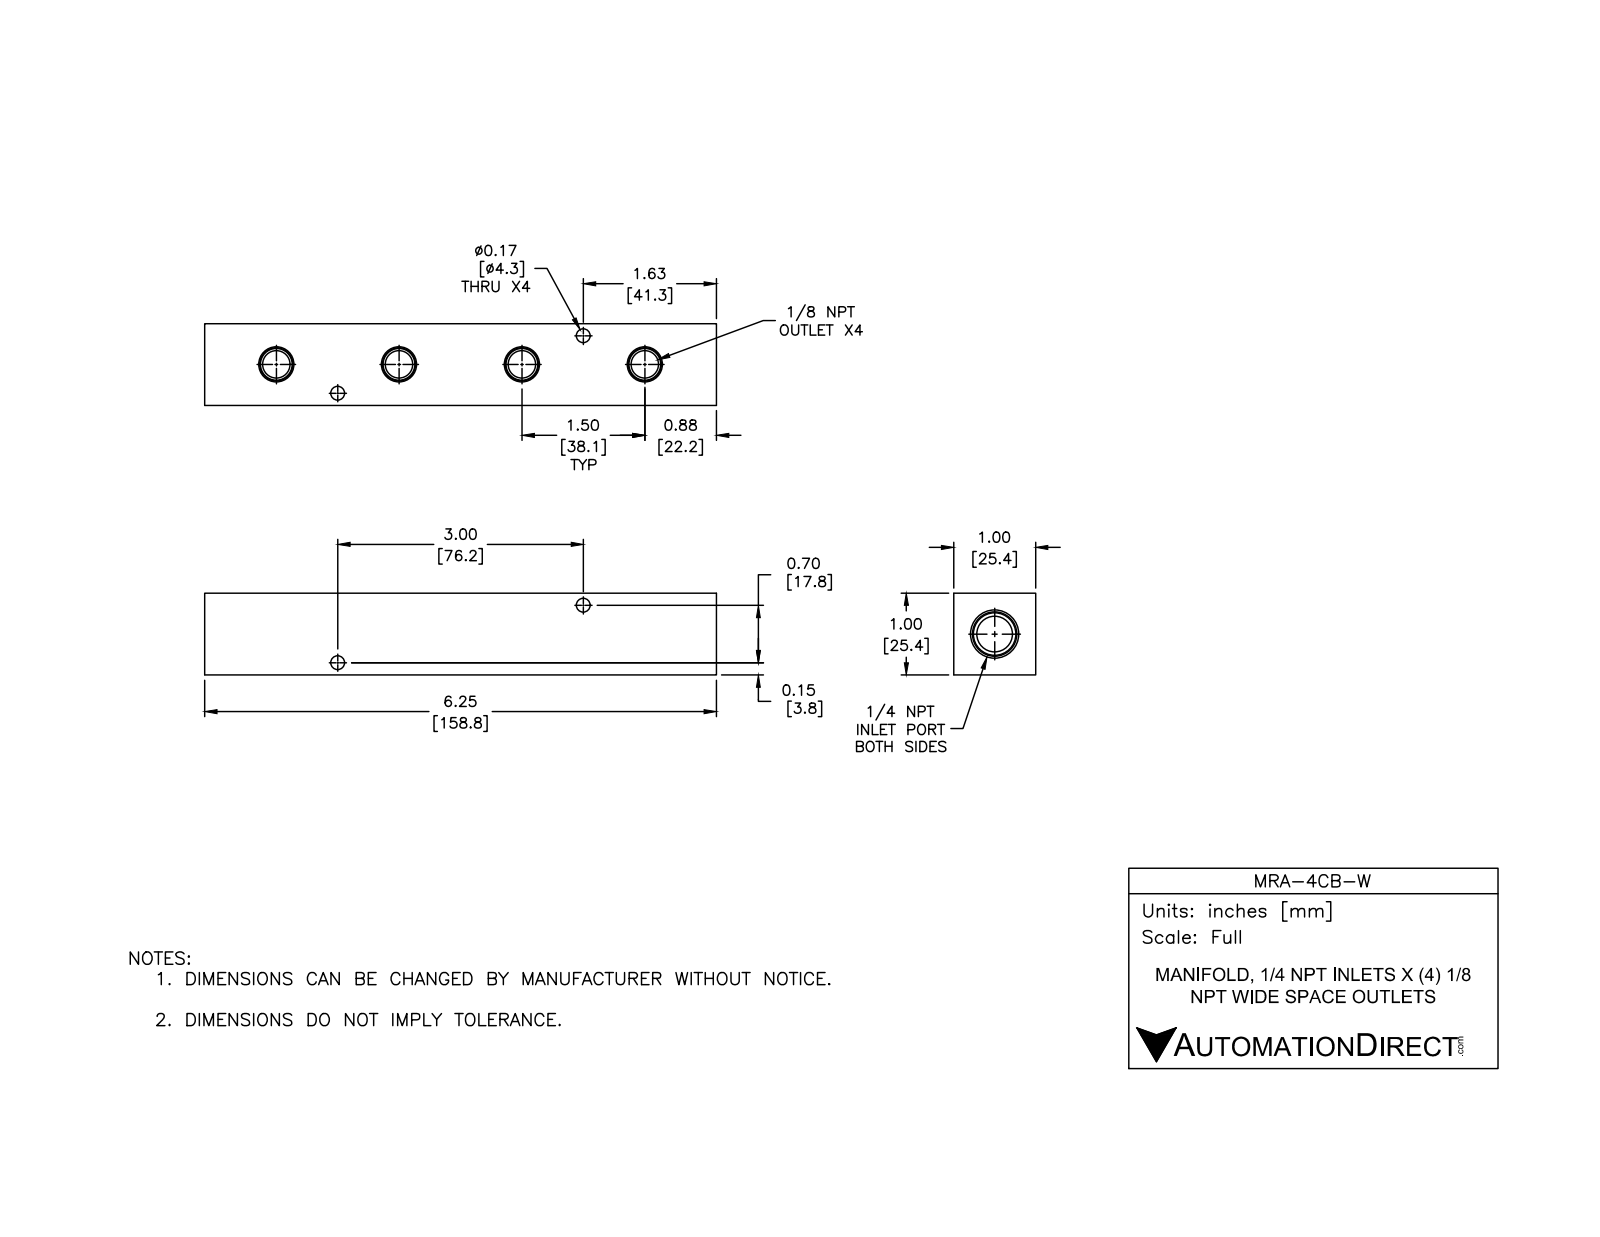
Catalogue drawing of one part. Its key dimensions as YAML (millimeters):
part_name: "MRA-4CB-W"
step_written_by: "SolidWorks 2015 (CONFIG_CONTROL_DESIGN)"
units: millimeters
bodies: {solids: 1, faces: 62, planar: 12, cylindrical: 26, other: 24}
overall_size: [158.8, 25.4, 25.4]
volume: 82330
surface_area: 24460
round_holes:
  - {diameter: 4.3, count: 4}
  - {diameter: 8.4, count: 4}
  - {diameter: 11.1, count: 1}
face_to_face_distances: [25.4, 158.8, 18.5, 6.9, 9.9, 148.8, 138.9]
hole_center_spacings: [21, 38.1, 57.8, 76.2, 78.3, 95.7, 114.3]
